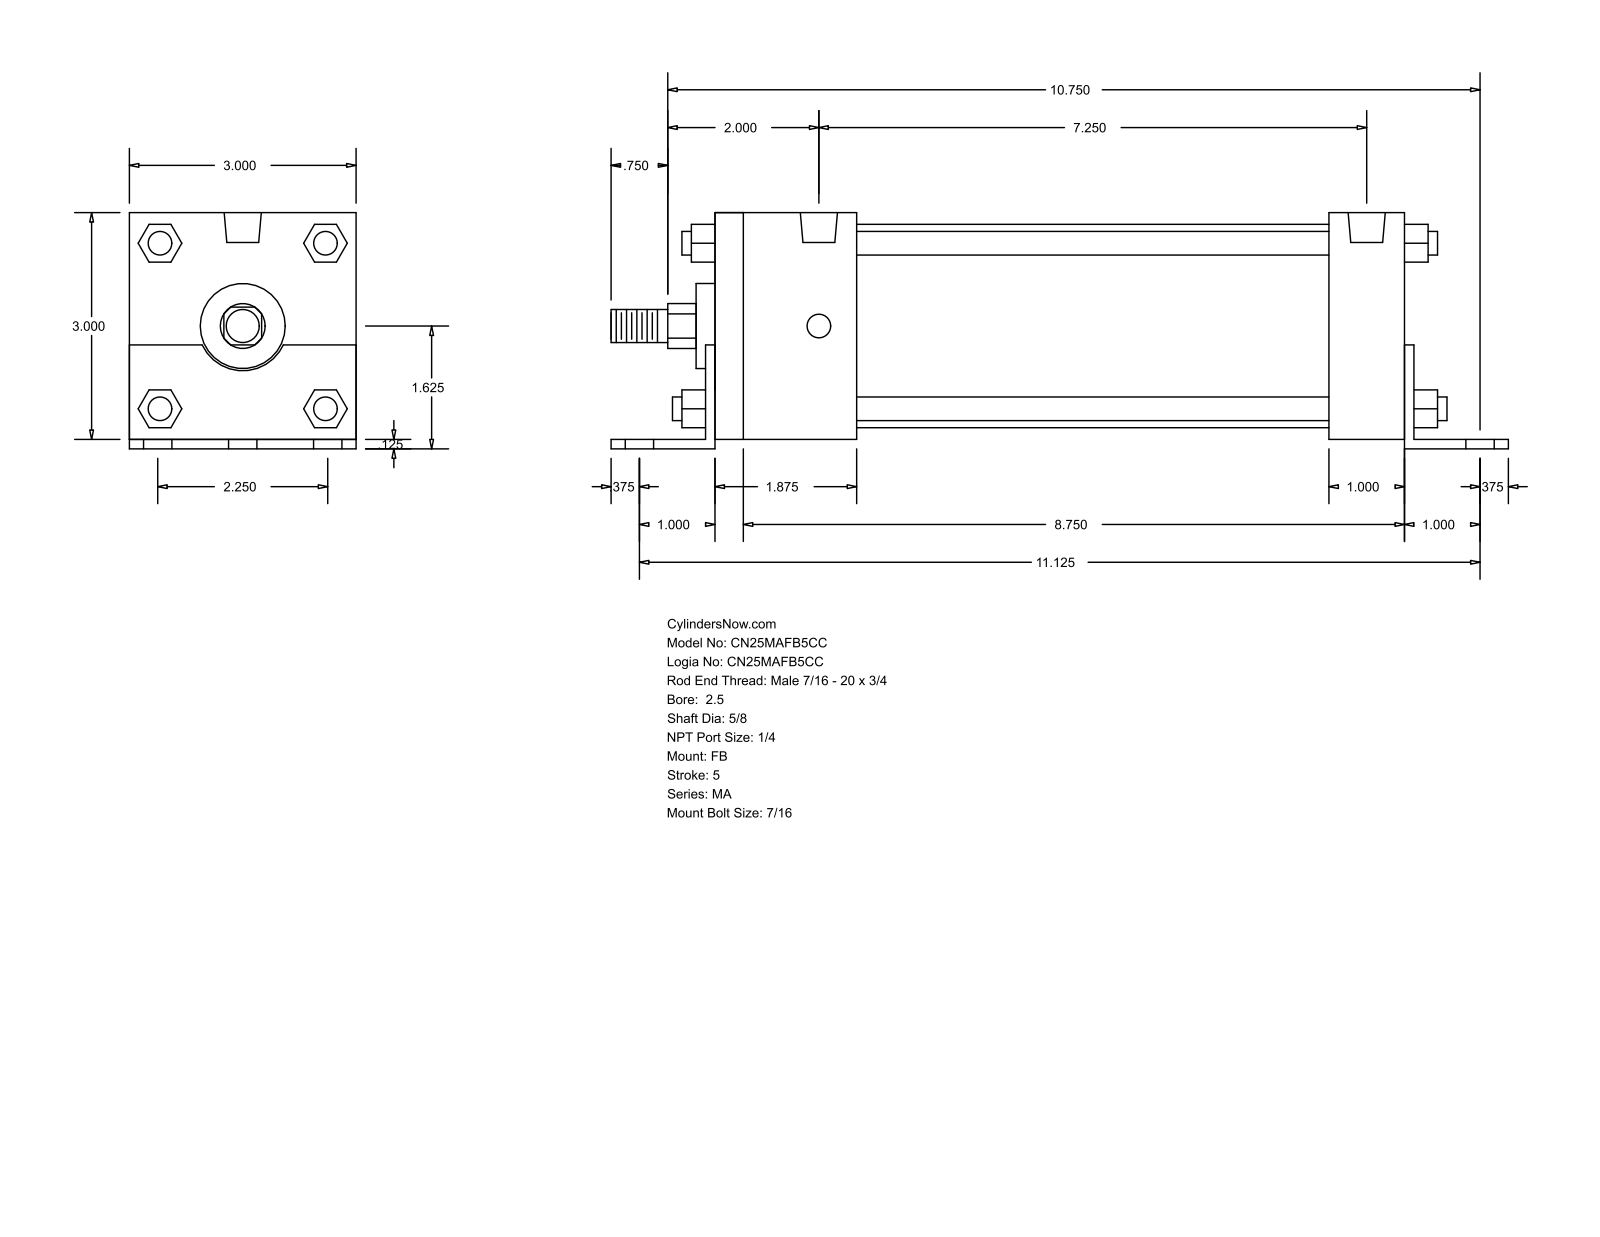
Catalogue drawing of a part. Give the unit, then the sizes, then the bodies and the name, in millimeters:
Units: millimetres
Overall size (bounding box): 301.62 × 79.38 × 76.2
Round holes (diameter × count): ⌀11.11 ×6, ⌀7.94 ×4, ⌀12.49 ×2
Round bosses / shafts (diameter × count): ⌀7.94 ×4, ⌀68.33 ×1, ⌀28.57 ×1, ⌀15.88 ×1, ⌀11.11 ×1
Partial cylindrical surfaces — rounded edges, fillets, slot ends (radius × count): R7.54 ×1, R15.05 ×1
Main face-to-face distances: 76.2, 3.17, 79.37, 231.77, 238.12, 3.18, 234.94, 47.62, 25.4, 234.95
Hole centre spacings: 28.57, 284.02, 282.58, 47.62, 57.14, 66.75, 184.15, 224.08
Bodies: 0 solids, 140 faces (105 planar, 35 cylindrical, 0 other)
Part name (STEP PRODUCT): MA_FB__0250_0.625
STEP written by: GSSL Pune (CONFIG_CONTROL_DESIGN)
